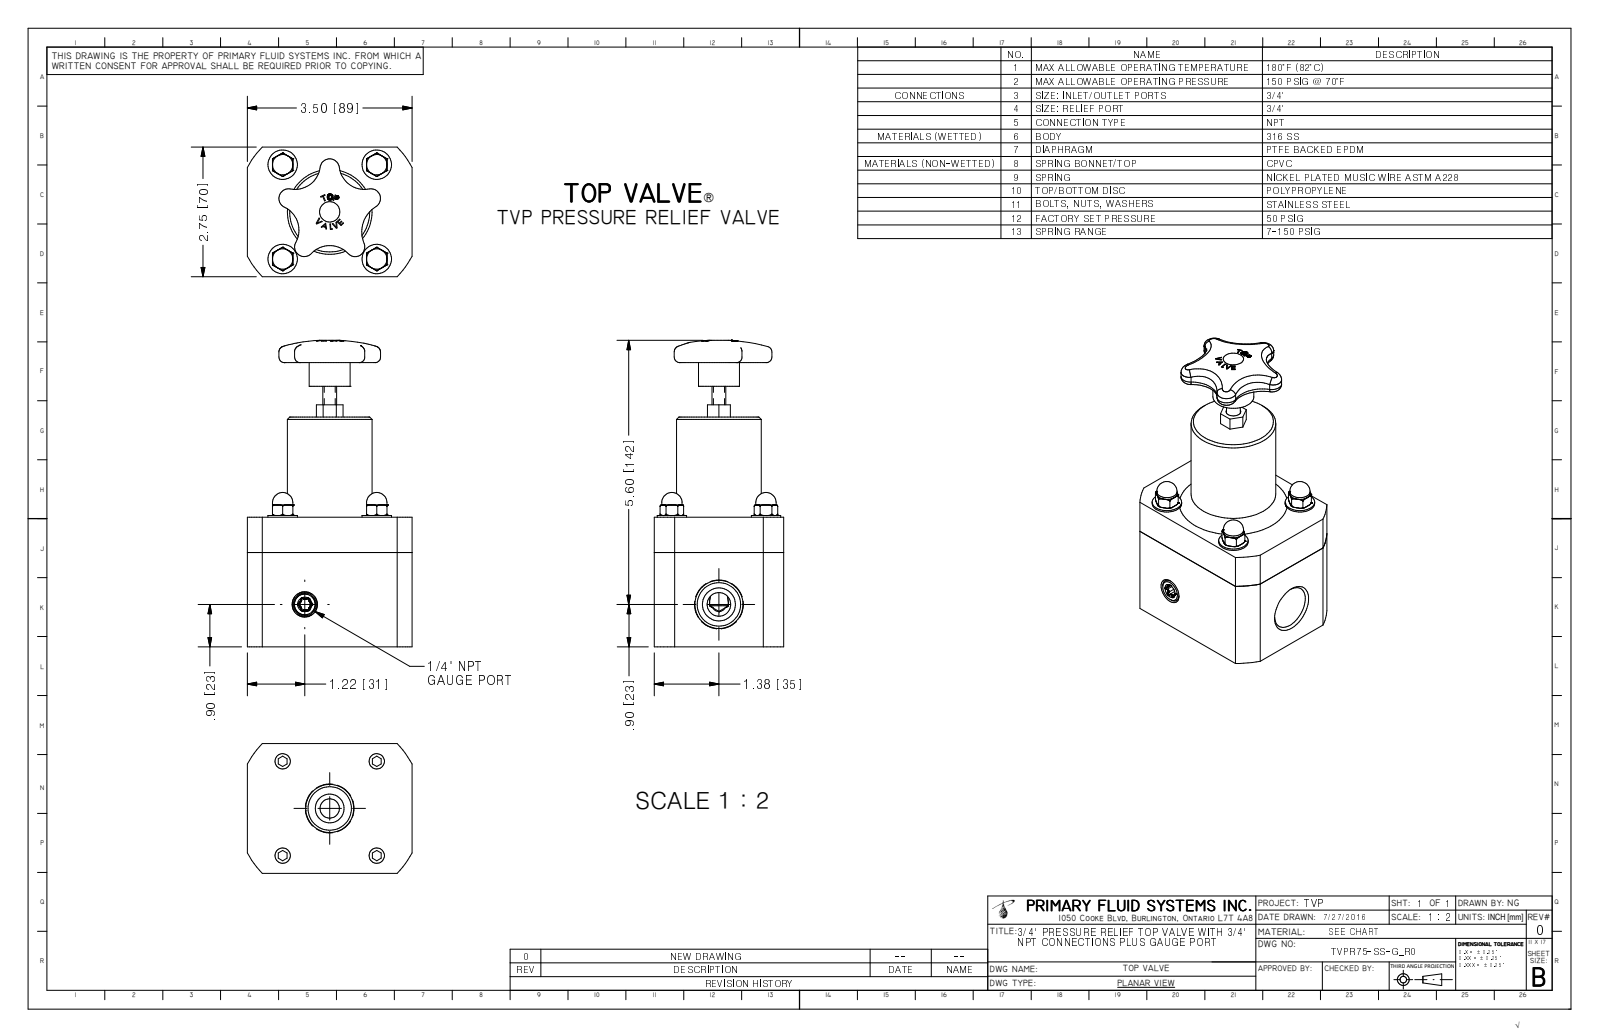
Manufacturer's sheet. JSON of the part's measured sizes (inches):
{"part_name": "TVPR75-SS-G_R0", "step_written_by": "Autodesk Inventor 2009 (AUTOMOTIVE_DESIGN)", "units": "inches", "bodies": {"solids": 1, "faces": 338, "planar": 131, "cylindrical": 50, "other": 157}, "overall_size": [6.5, 3.5, 2.75], "volume_in3": 31.34, "surface_area_in2": 83.37, "round_holes": [[0.175, 4], [0.922, 2], [2.4, 1]], "round_bosses_or_shafts": [[0.625, 4], [0.433, 4], [2.375, 1], [1.8, 1], [0.87, 1], [0.293, 1]], "partial_cylinders_radius": [[0.027, 6], [0.085, 5], [0.205, 5], [0.536, 4], [0.656, 4], [0.625, 1], [0.745, 1], [1.988, 1]], "face_to_face_distances": [2.75, 2.75, 3.5, 4.875, 2.125, 0.75, 2, 0.6, 2.15, 4.275], "hole_center_spacings": [1.414, 2, 2.828]}
